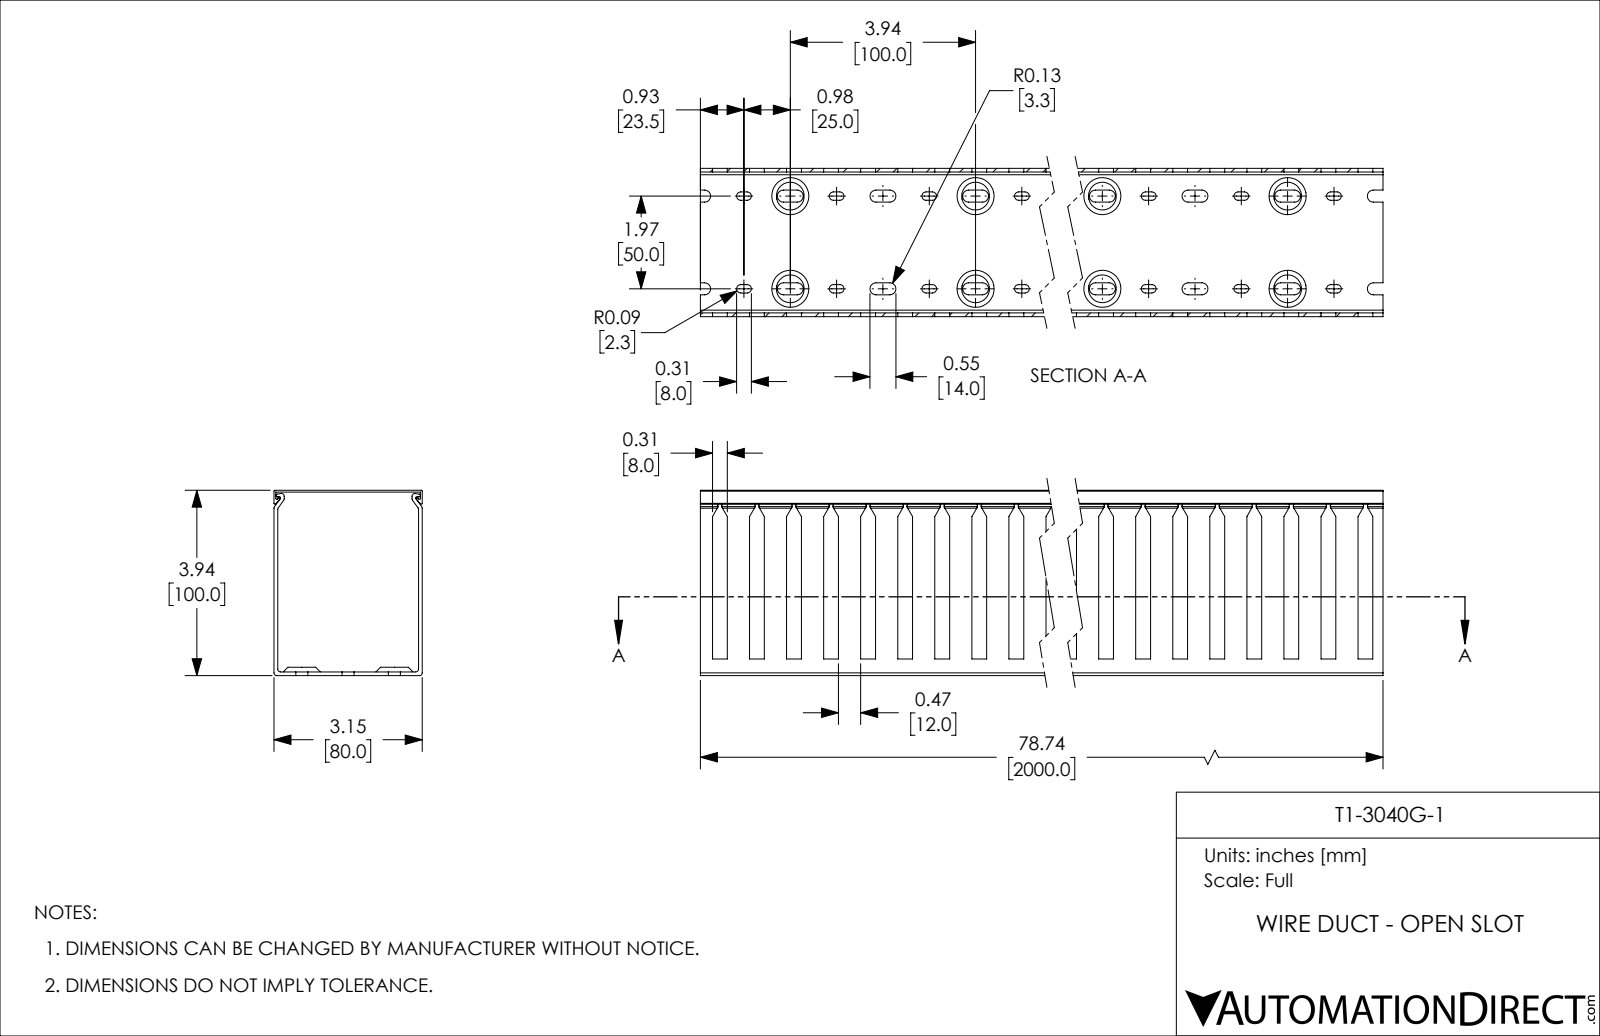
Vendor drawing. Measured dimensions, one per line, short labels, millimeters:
name: T1-3040G-1
written by: SolidWorks 2021 (CONFIG_CONTROL_DESIGN)
unit: mm
bodies: 2 solids, 1573 faces (762 planar, 731 cylindrical, 80 other)
size: 2000 × 100 × 80
volume: 1 278 000 mm³; area: 1 479 000 mm²
rounds: 200× R3.25, 160× R2.25, 12× R1.5, 8× R0.5, 6× R0.75
face distances: 2, 78, 80, 1, 76, 100, 99, 97, 98, 79
